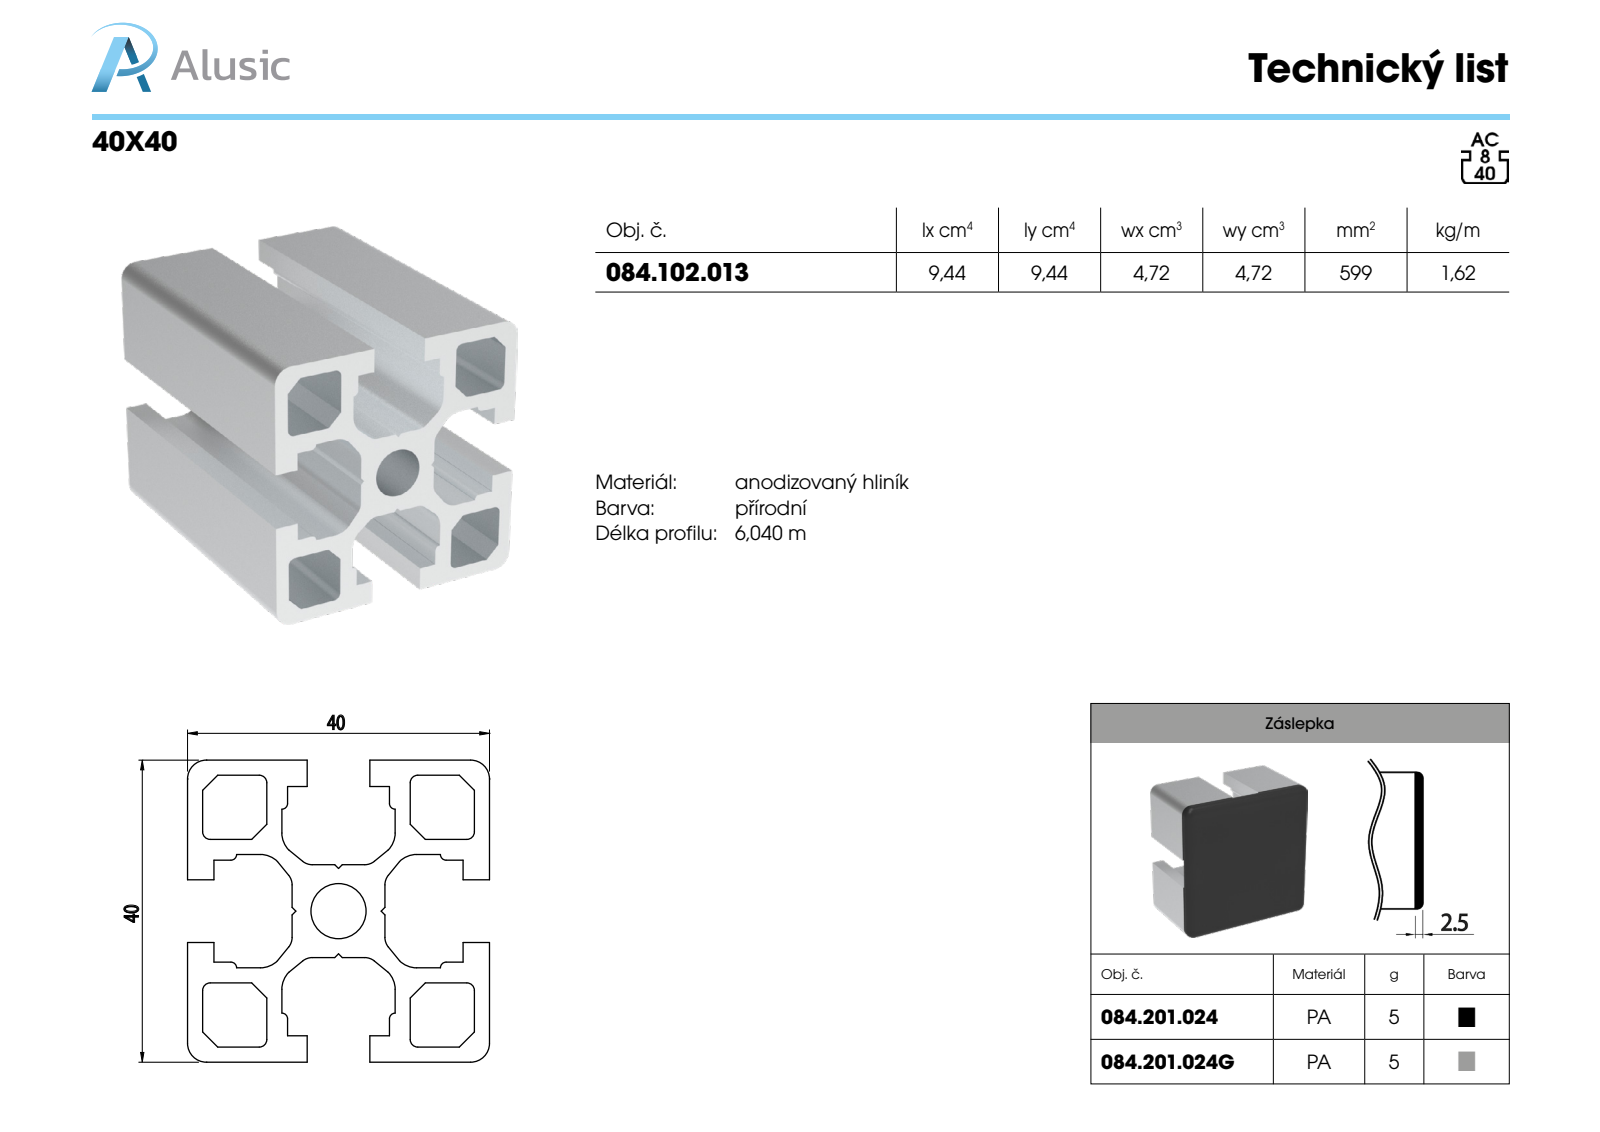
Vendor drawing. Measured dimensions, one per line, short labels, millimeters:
name: 084.102.013
written by: SolidWorks 2012 (CONFIG_CONTROL_DESIGN)
unit: mm
bodies: 1 solid, 128 faces (90 planar, 38 cylindrical, 0 other)
size: 50 × 40 × 40
volume: 29 939 mm³; area: 23 667 mm²
holes: 1× ⌀7.3
rounds: 8× R0.75, 8× R1, 8× R2, 8× R3.2, 4× R2.5
face distances: 2, 10.5, 27.5, 40, 24.15, 13.65, 13.85, 3.35, 38, 29.5
